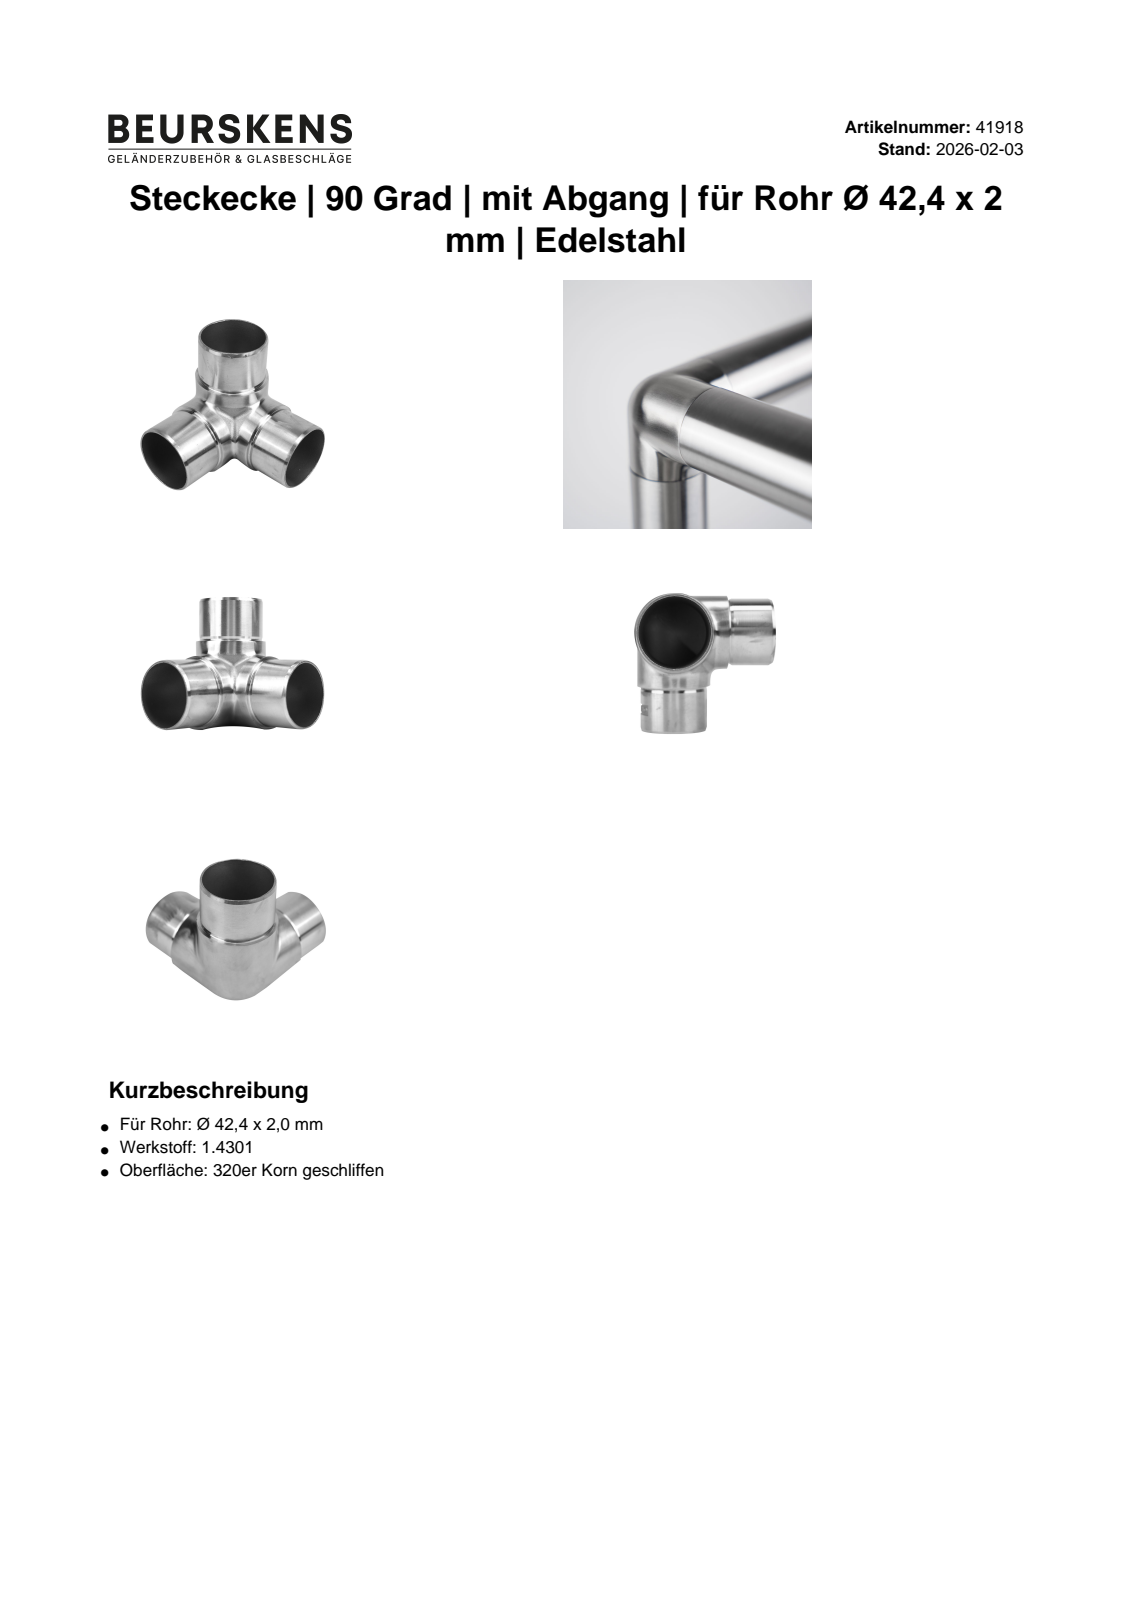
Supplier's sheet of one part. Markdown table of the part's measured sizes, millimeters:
| quantity | value |
| --- | --- |
| part name | 41918 |
| STEP written by | Autodesk Inventor 2022 (AUTOMOTIVE_DESIGN) |
| units | millimeters |
| bodies | 1 solid, 23 faces (9 planar, 12 cylindrical, 2 other) |
| overall size | 76.49 × 76.2 × 76.2 |
| volume | 34 270 mm³ |
| surface area | 34 946 mm² |
| round holes (diameter × count) | 34.4 × 3, 38.4 × 3 |
| round bosses / shafts (diameter × count) | 42.4 × 3, 38.4 × 1 |
| main face-to-face distances | 2, 25, 27, 25.01, 27.01 |
